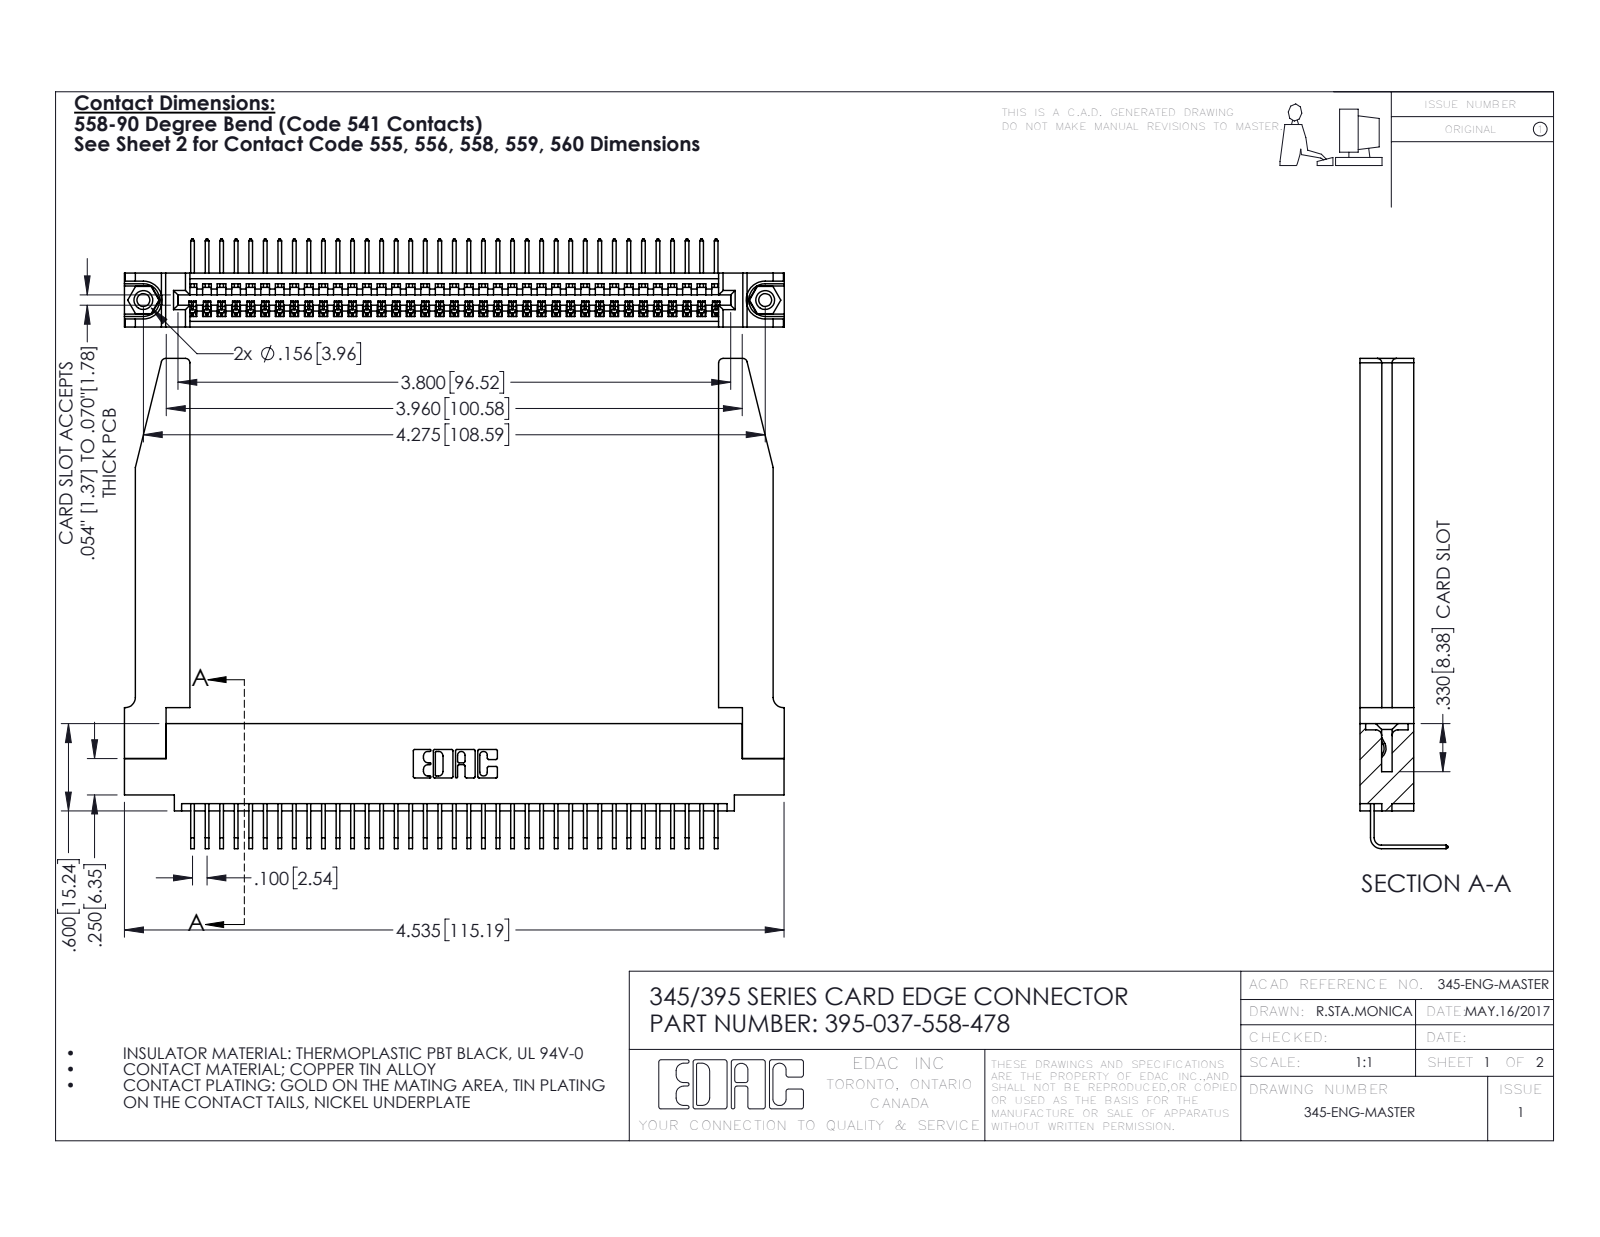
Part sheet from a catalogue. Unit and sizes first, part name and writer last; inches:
Units: inches
Overall size (bounding box): 4.536 × 3.369 × 0.605
Round holes (diameter × count): ⌀0.089 ×2, ⌀0.125 ×2, ⌀0.156 ×2, ⌀0.064 ×1
Round bosses / shafts (diameter × count): ⌀0.155 ×2
Partial cylindrical surfaces — rounded edges, fillets, slot ends (radius × count): R0.006 ×74, R0.01 ×22, R0.03 ×8, R0.007 ×6, R0.031 ×6, R0.026 ×3, R0.031 ×2, R0.04 ×2
Main face-to-face distances: 0.37, 0.072, 0.298, 0.098, 0.272, 0.025, 0.2, 0.225, 0.15, 0.148
Hole centre spacings: 0.27, 4.039, 4.275
Volume: 1.143 in³ · Surface area: 34.31 in²
Bodies: 42 solids, 2584 faces (1780 planar, 752 cylindrical, 52 other)
Part name (STEP PRODUCT): 345-250-001_345-250-001-102; 345-220-078_345-220-078; 345 Part_0.110 Offset - 0.156 Dia-TH; 345-292-001_558 Tail - 2 (+1 more)
STEP written by: SolidWorks 2016 (CONFIG_CONTROL_DESIGN)
